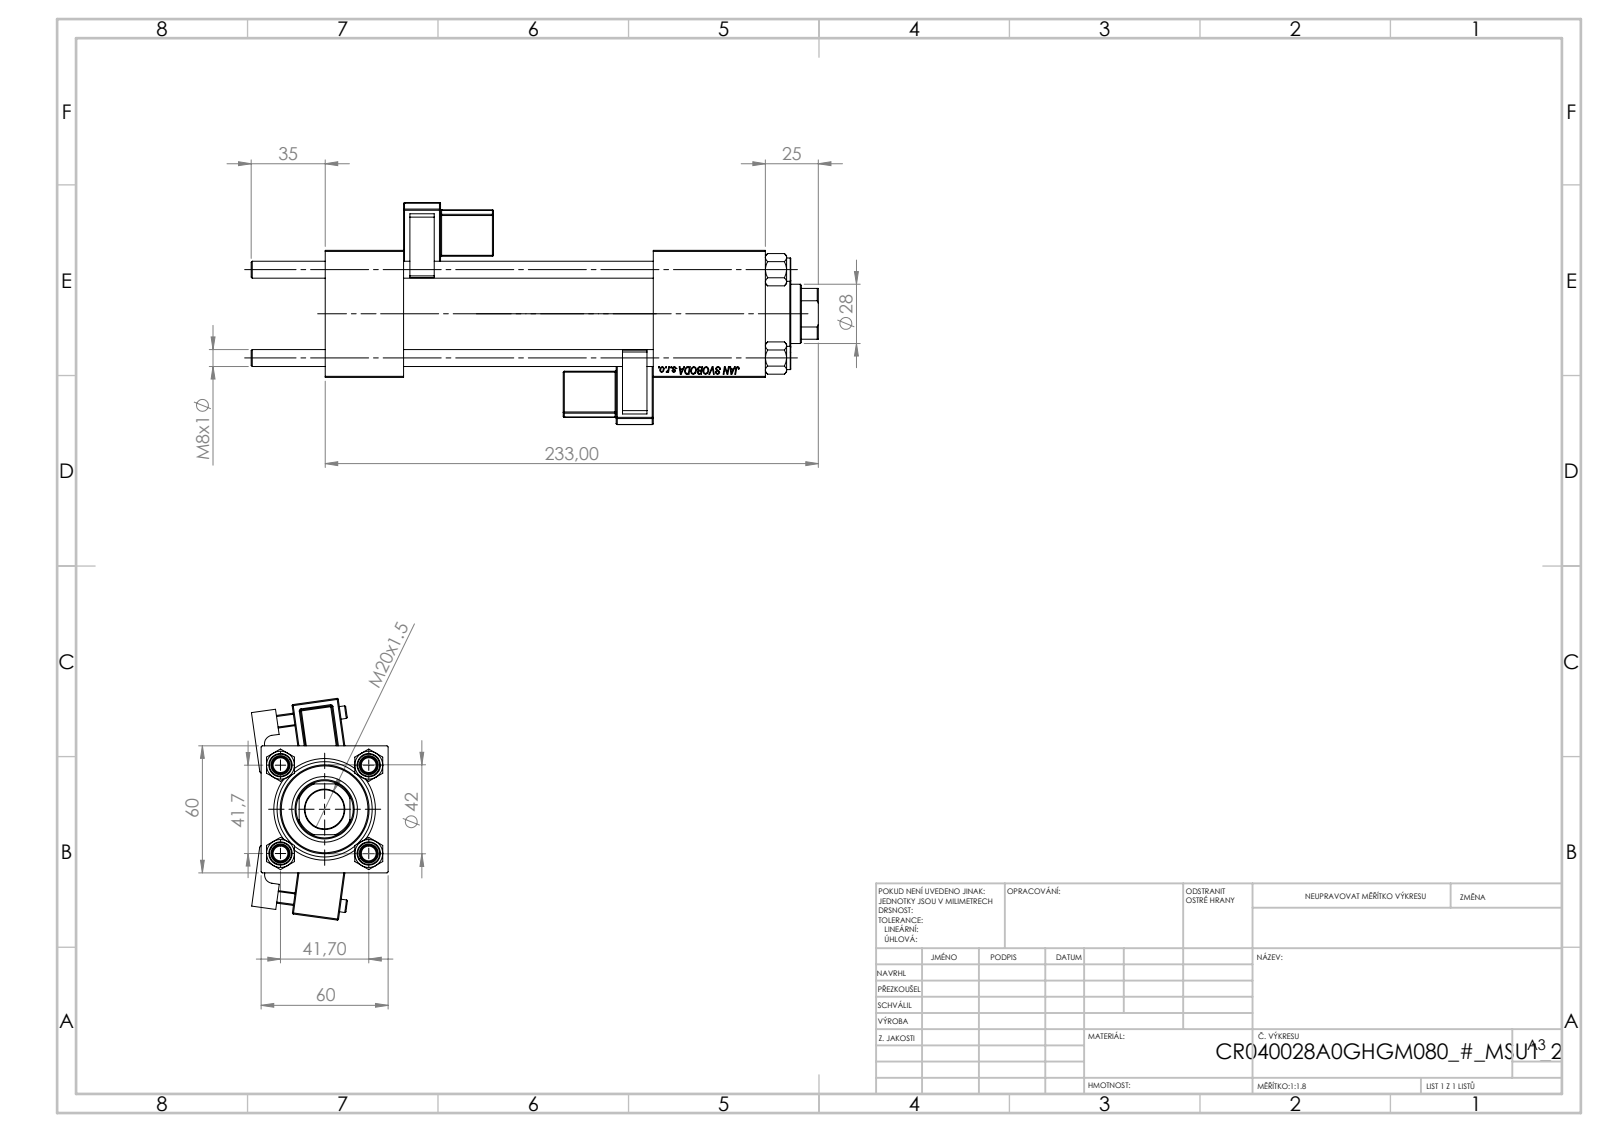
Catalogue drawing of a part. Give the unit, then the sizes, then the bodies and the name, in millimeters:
Units: millimetres
Overall size (bounding box): 268 × 104.69 × 64.58
Round holes (diameter × count): ⌀8 ×4, ⌀7 ×2, ⌀16.66 ×2, ⌀24 ×2, ⌀18.5 ×1, ⌀28 ×1, ⌀31 ×1, ⌀40 ×1, ⌀45 ×1
Round bosses / shafts (diameter × count): ⌀11 ×4, ⌀6 ×2, ⌀46 ×1, ⌀42 ×1
Partial cylindrical surfaces — rounded edges, fillets, slot ends (radius × count): R0.5 ×48, R1 ×2, R2.5 ×2, R4 ×2, R13.5 ×1
Main face-to-face distances: 60, 37, 155, 118, 53, 208, 171, 179.3, 142.3, 24.3
Hole centre spacings: 29.49, 41.7, 58.97, 152.5
Volume: 549 675 mm³ · Surface area: 159 716 mm²
Bodies: 13 solids, 1289 faces (579 planar, 138 cylindrical, 572 other)
Part name (STEP PRODUCT): V215_VC_A; CR025_012_A_0_G_A_G_M_020_+#_##_TYCINKA; NUT_M5; V215CR_BODY_A (+2 more)
STEP written by: SolidWorks 2019 (CONFIG_CONTROL_DESIGN)
